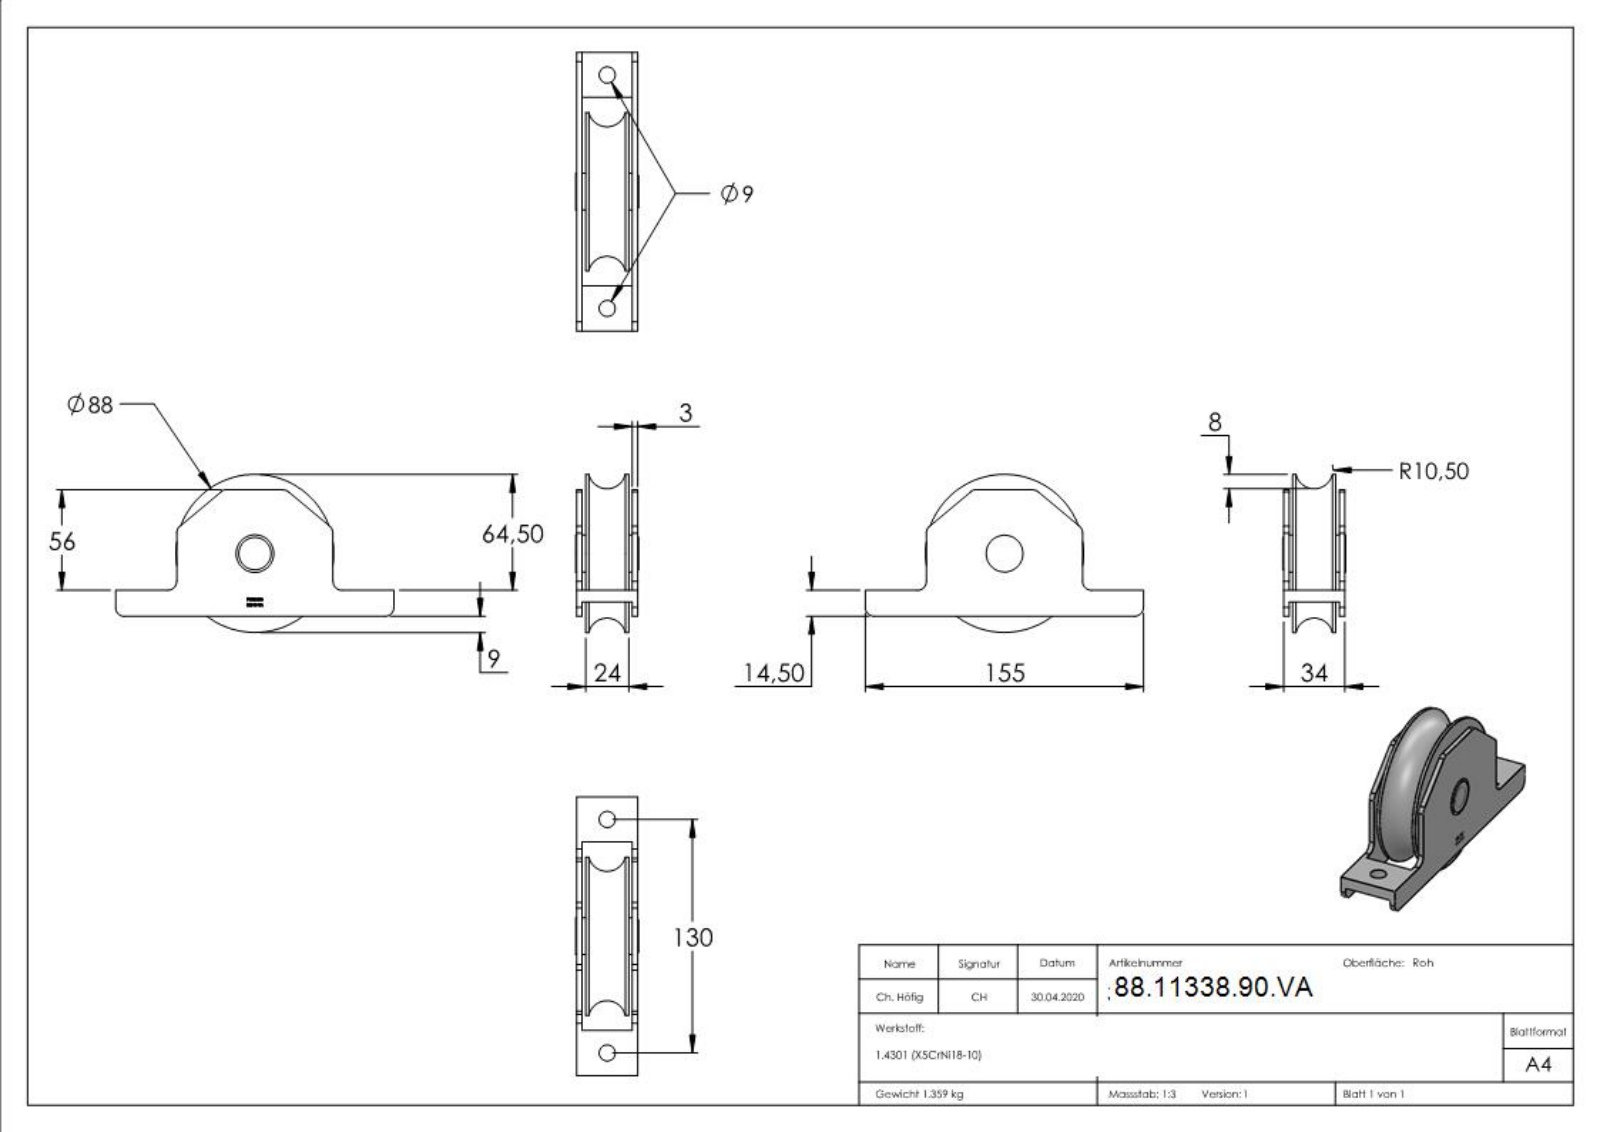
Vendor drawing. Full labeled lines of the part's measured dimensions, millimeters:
Part name (STEP PRODUCT): 338-90-VA
STEP written by: SolidWorks 2015 (CONFIG_CONTROL_DESIGN)
Units: millimetres
Bodies: 2 solids, 280 faces (143 planar, 23 cylindrical, 114 other)
Overall size (bounding box): 155 × 88 × 35
Volume: 171 963 mm³ · Surface area: 53 201 mm²
Round holes (diameter × count): ⌀9 ×2
Round bosses / shafts (diameter × count): ⌀88 ×1, ⌀20.5 ×1, ⌀18 ×1
Partial cylindrical surfaces — rounded edges, fillets, slot ends (radius × count): R5 ×8
Main face-to-face distances: 5, 29, 3, 31, 2, 26, 34, 24, 28, 6.5
Hole centre spacings: 130
